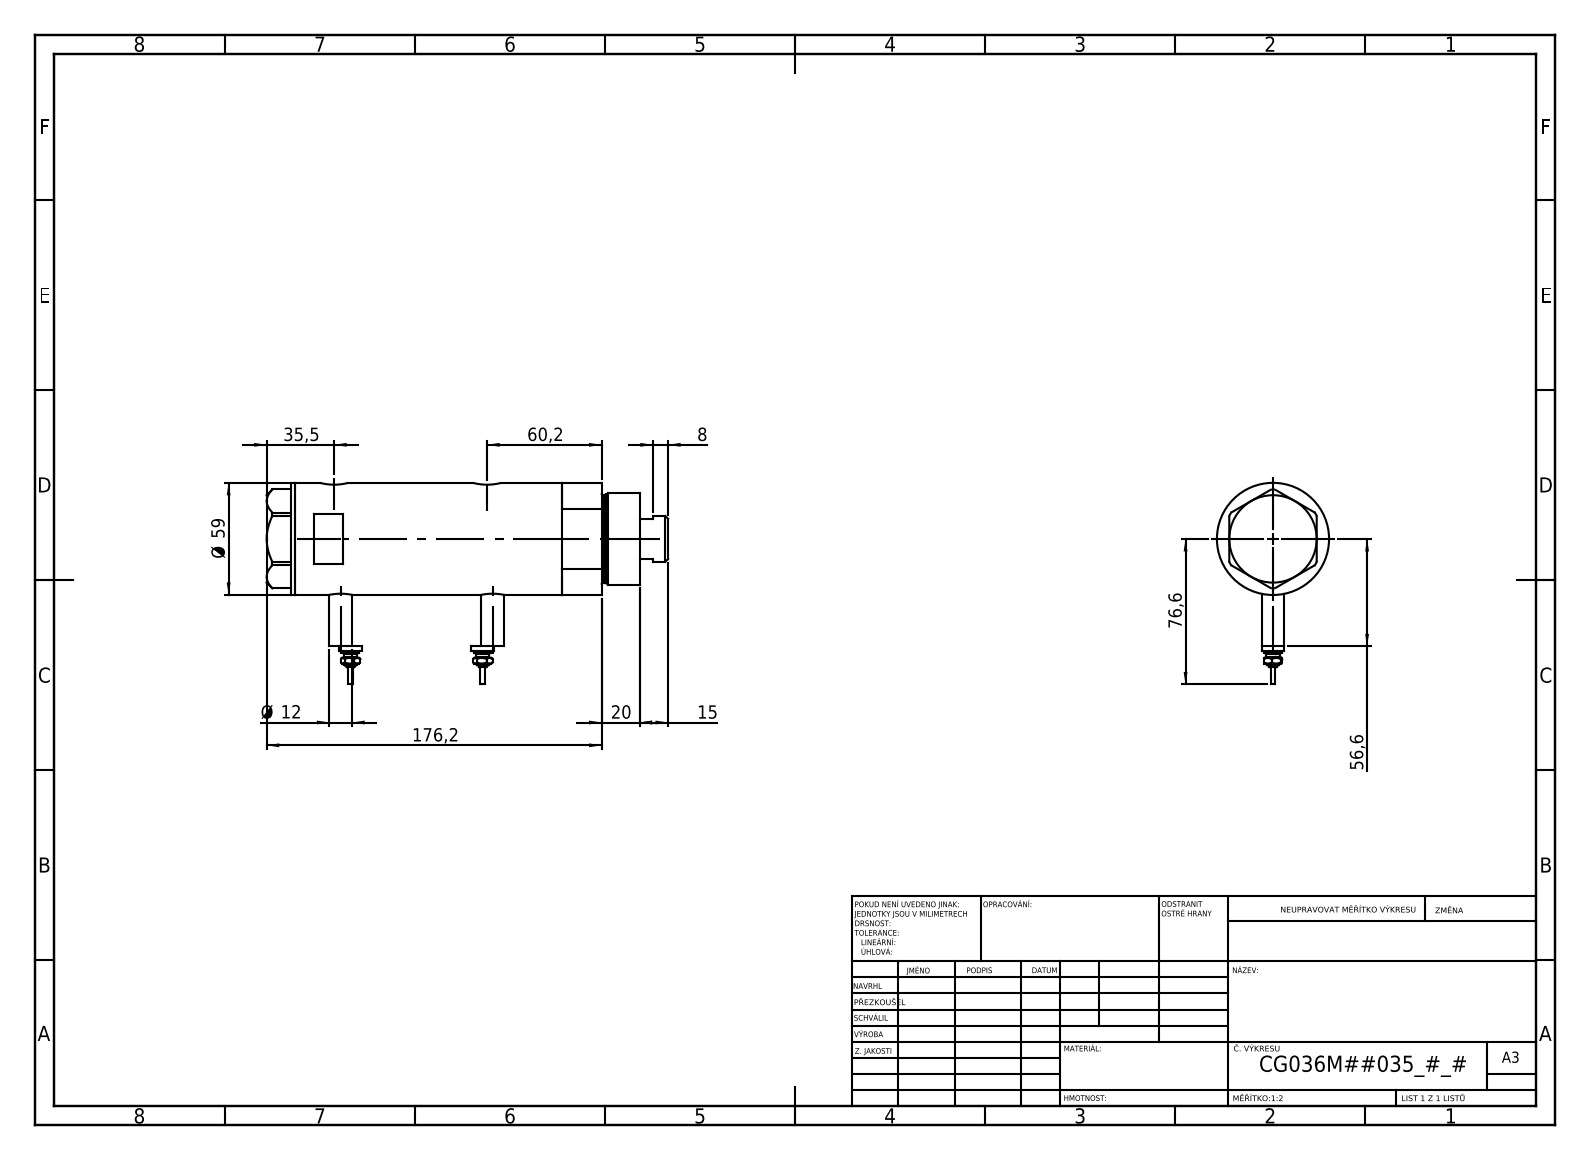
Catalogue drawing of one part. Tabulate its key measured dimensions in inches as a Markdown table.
| quantity | value |
| --- | --- |
| part name | V270CG_BACK; V270CG_FRONT; V270CG_MIDDLE; V270CG_VC (+1 more) |
| STEP written by | SolidWorks 2019 (CONFIG_CONTROL_DESIGN) |
| units | inches |
| bodies | 6 solids, 212 faces (79 planar, 69 cylindrical, 64 other) |
| overall size | 8.315 × 4.177 × 2.323 |
| volume | 30.05 in³ |
| surface area | 160.1 in² |
| round holes (diameter × count) | 0.383 × 2, 0.492 × 2, 0.591 × 2, 0.335 × 1, 0.984 × 1, 1.043 × 1, 1.417 × 1, 1.575 × 1, 2.047 × 1 |
| round bosses / shafts (diameter × count) | 0.472 × 4, 0.354 × 2, 0.276 × 2, 0.177 × 2, 0.098 × 2, 2.323 × 1, 1.89 × 1, 1.811 × 1 |
| main face-to-face distances | 4.024, 0.925, 3.098, 0.591, 1.516, 4.614, 0.079, 7.724, 7.134, 6.209 |
| hole center spacings | 0.114, 0.138, 3.031, 3.146, 3.169, 3.283 |
